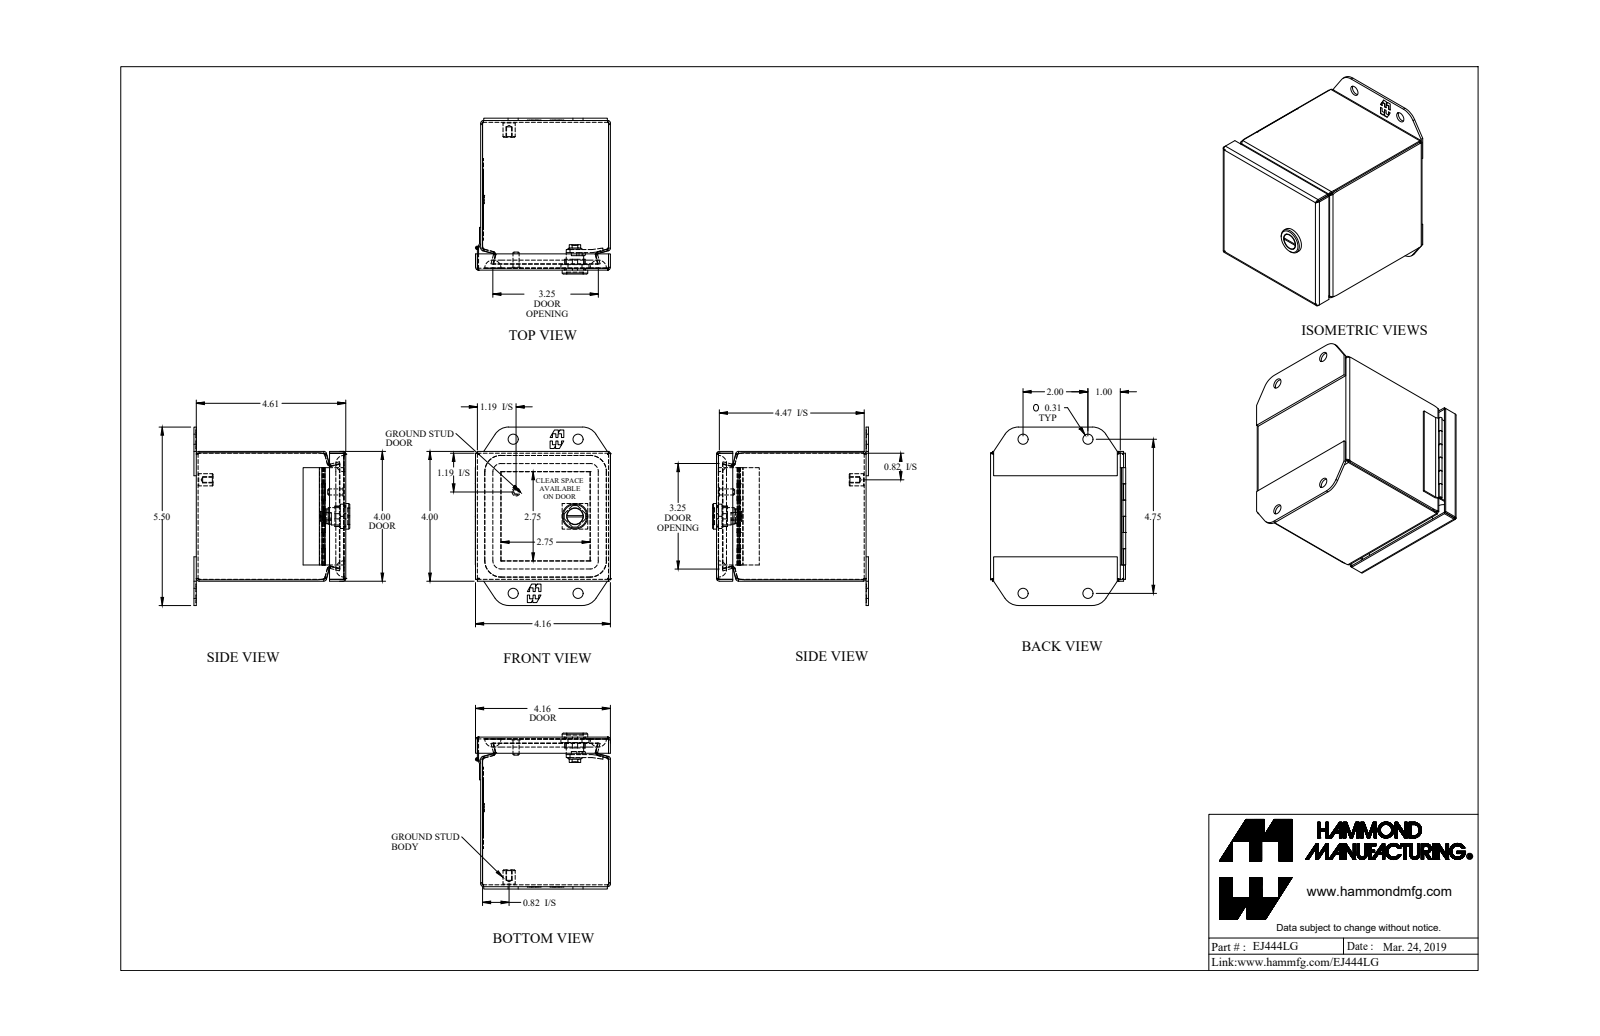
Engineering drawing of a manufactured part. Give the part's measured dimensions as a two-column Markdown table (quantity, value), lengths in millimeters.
| quantity | value |
| --- | --- |
| part name | EJ444LG_Default |
| STEP written by | SolidWorks 2019 (CONFIG_CONTROL_DESIGN) |
| units | millimeters |
| bodies | 11 solids, 517 faces (315 planar, 134 cylindrical, 68 other) |
| overall size | 139.7 × 122 × 105.8 |
| volume | 142 400 mm³ |
| surface area | 186 600 mm² |
| round holes (diameter × count) | 8 × 4, 1.3 × 1, 4 × 1, 13.1 × 1 |
| round bosses / shafts (diameter × count) | 20 × 1, 13.6 × 1, 12.6 × 1, 11 × 1, 9.5 × 1, 6.4 × 1, 4.8 × 1, 2.5 × 1 |
| partial cylindrical surfaces (radius × count) | 0.7 × 16, 2.2 × 16, 7.1 × 10, 6.4 × 4, 12.7 × 4, 12.7 × 4, 1.5 × 2, 13.7 × 2 |
| main face-to-face distances | 1.4, 100.2, 115.7, 98.7, 101.6, 117.1, 114.2, 118.9, 117.5, 3.3 |
| hole center spacings | 50.8, 60.4, 77.4, 120.7, 130.9, 31.9, 59, 62.6 |
